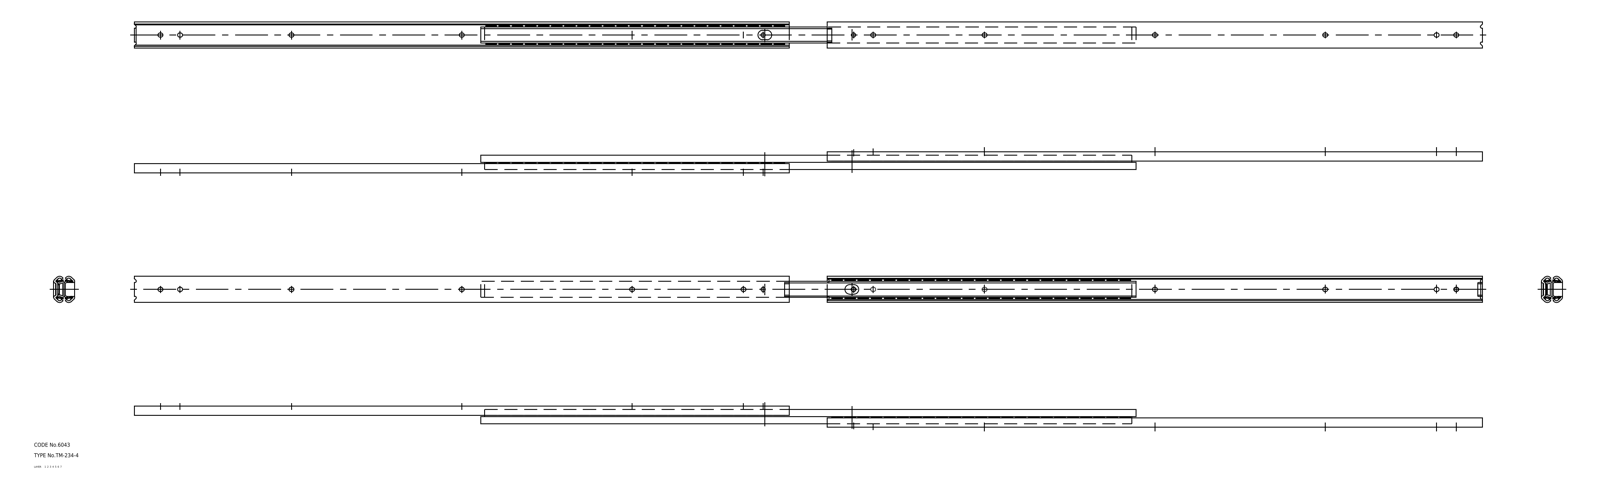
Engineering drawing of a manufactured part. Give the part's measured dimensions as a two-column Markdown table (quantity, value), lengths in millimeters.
| quantity | value |
| --- | --- |
| part name | ball; retainer; member_A; member_B (+1 more) |
| STEP written by | CADfix (AUTOMOTIVE_DESIGN) |
| units | millimeters |
| bodies | 97 solids, 1240 faces (0 planar, 0 cylindrical, 1240 other) |
| overall size | 1029 × 20 × 16 |
| volume | 67 616 mm³ |
| surface area | 114 623 mm² |
